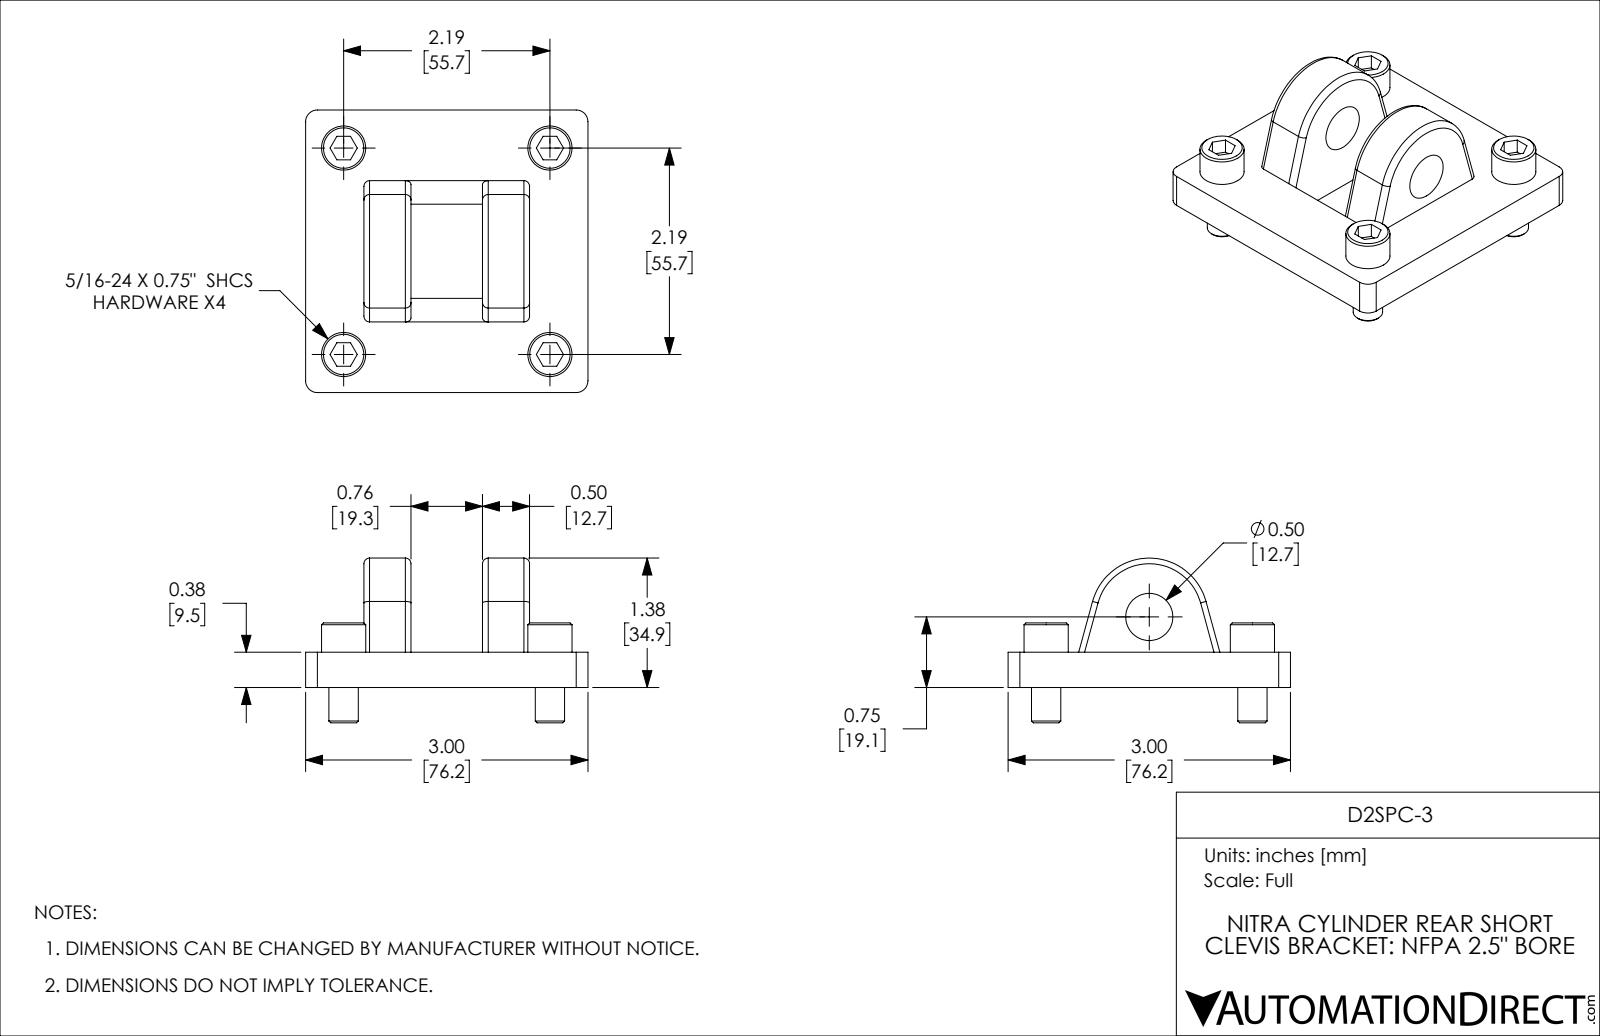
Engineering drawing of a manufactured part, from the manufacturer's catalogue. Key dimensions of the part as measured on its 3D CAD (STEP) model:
Part name (STEP PRODUCT): D2SPC-3
STEP written by: SolidWorks 2019 (CONFIG_CONTROL_DESIGN)
Units: inches
Bodies: 5 solids, 122 faces (56 planar, 46 cylindrical, 20 other)
Overall size (bounding box): 3 × 3 × 1.75
Volume: 4.224 in³ · Surface area: 35.91 in²
Round holes (diameter × count): ⌀0.344 ×4, ⌀0.501 ×1
Round bosses / shafts (diameter × count): ⌀0.469 ×4, ⌀0.312 ×4
Partial cylindrical surfaces — rounded edges, fillets, slot ends (radius × count): R0.06 ×8, R0.125 ×4, R0.625 ×1, R0.839 ×1
Main face-to-face distances: 0.375, 1.12, 1.88, 3, 0.62, 2.38, 0.5, 1.26, 0.76, 1.76
Hole centre spacings: 2.192, 3.1
